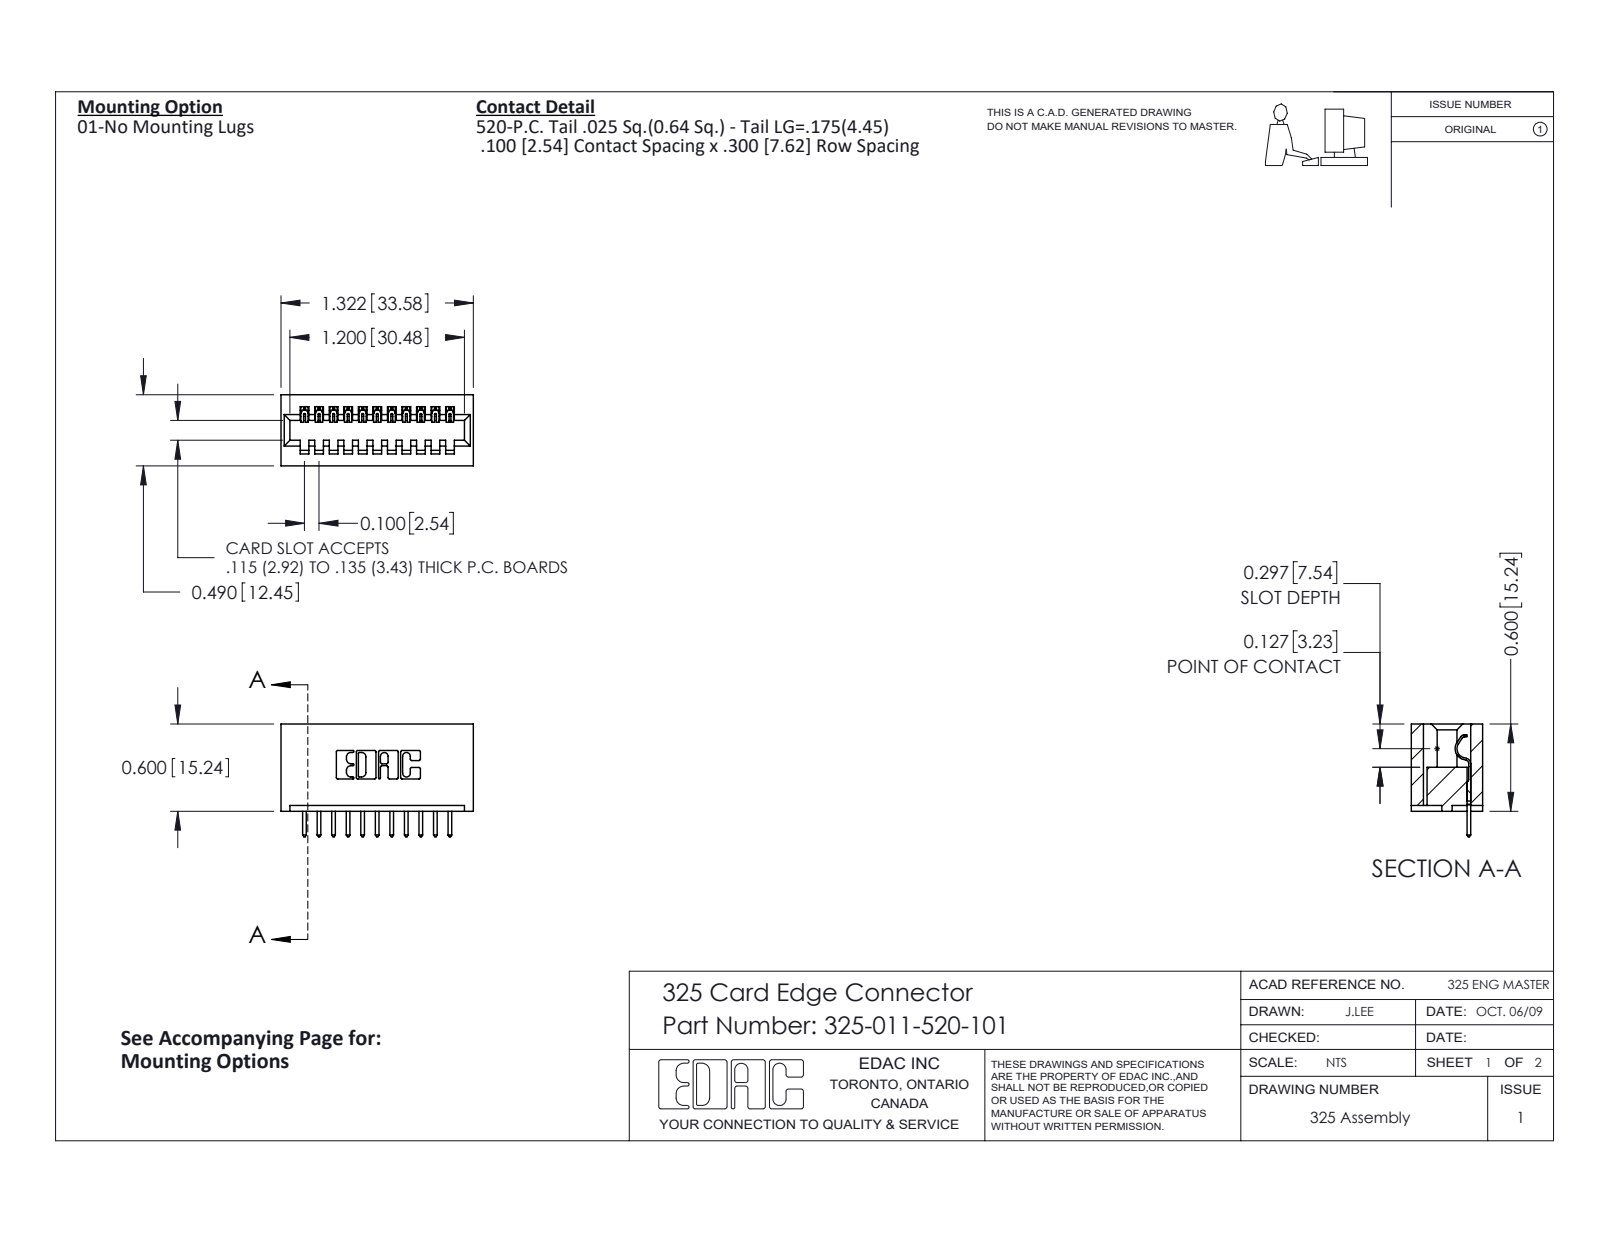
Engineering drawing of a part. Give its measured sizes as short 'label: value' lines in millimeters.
name: 325 Part_Lugless; 325-292-001_325-293-120; 325-011-520-101
written by: SolidWorks 2016 (CONFIG_CONTROL_DESIGN)
unit: mm
bodies: 12 solids, 744 faces (528 planar, 216 cylindrical, 0 other)
size: 33.6 × 19.7 × 12.4
volume: 4 560 mm³; area: 4 833 mm²
rounds: 22× R0.2, 22× R0.3, 22× R0.3, 6× R0.2, 6× R0.8, 3× R0.7, 1× R0.4, 1× R0.6
face distances: 7.6, 2.5, 2.1, 10.3, 5.1, 12.4, 10.2, 1, 15.2, 1.5
